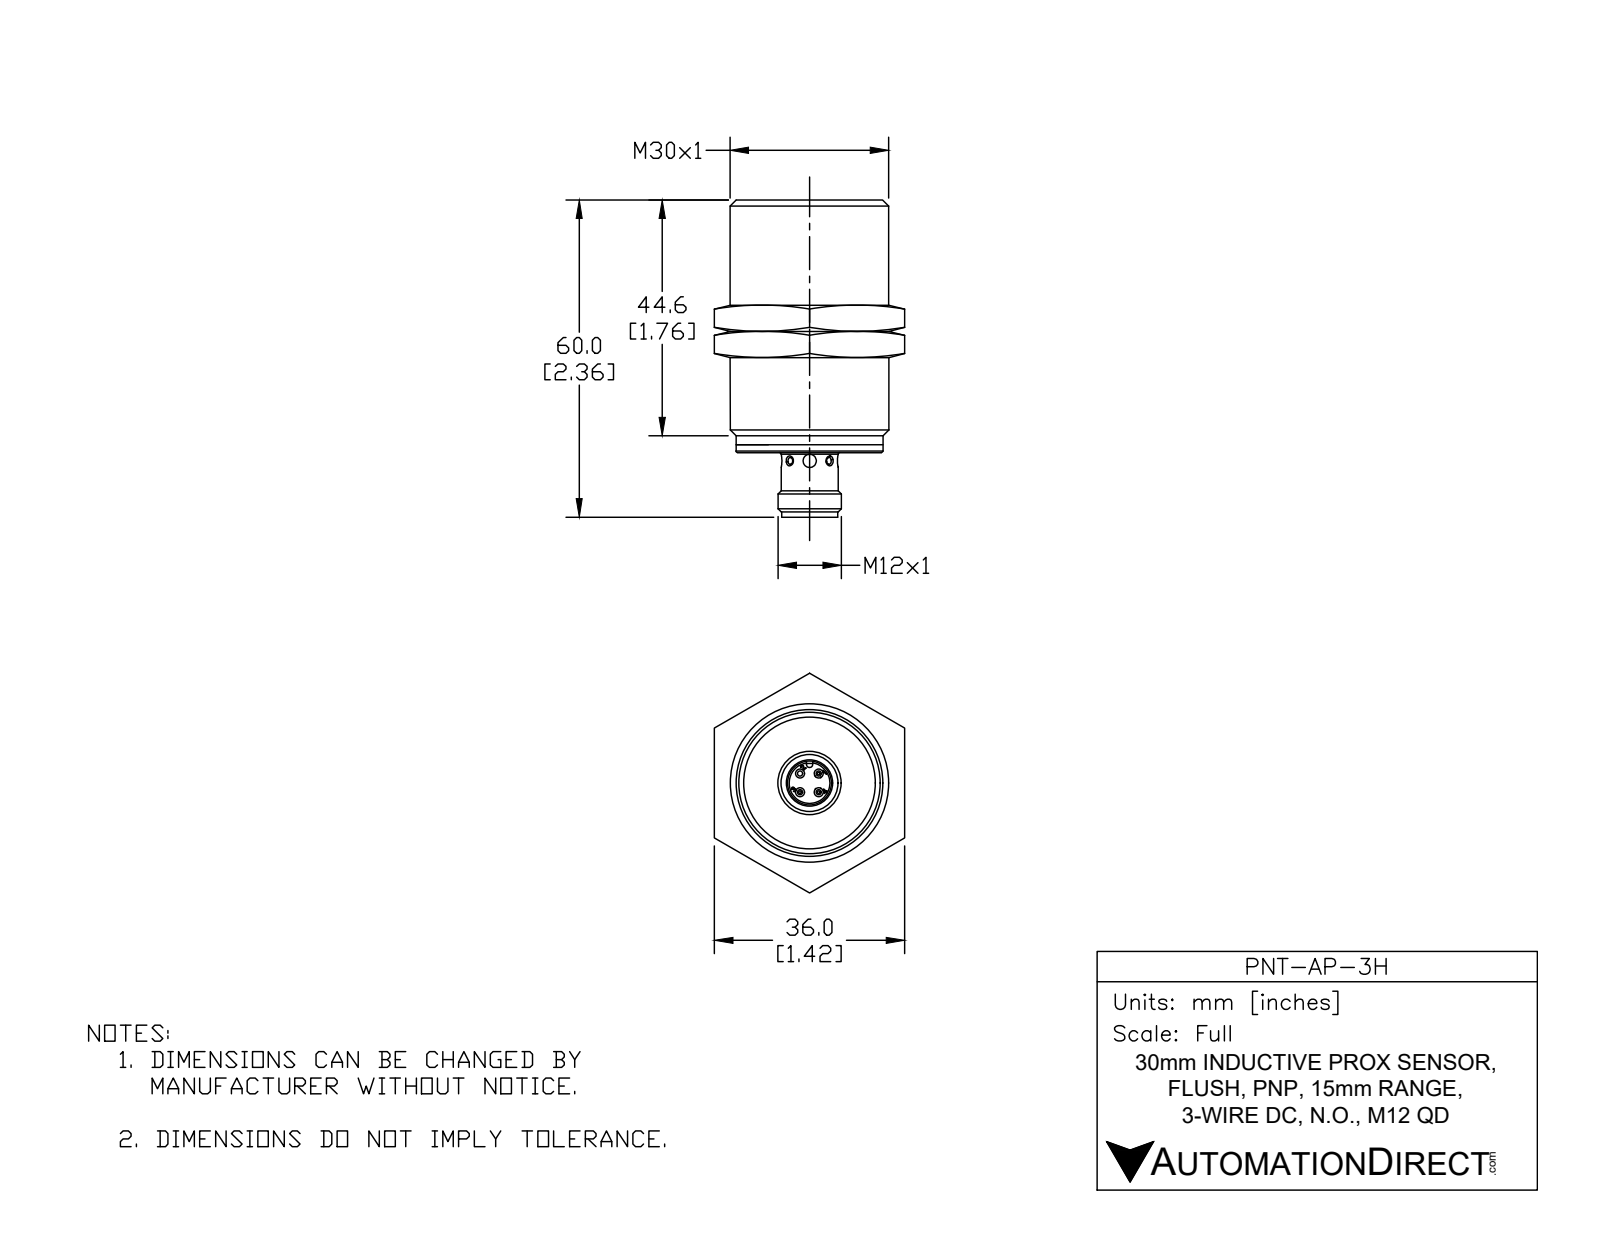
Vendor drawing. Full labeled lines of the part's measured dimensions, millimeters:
Part name (STEP PRODUCT): PNT-AP-3H
STEP written by: SolidWorks 2017 (AUTOMOTIVE_DESIGN)
Units: millimetres
Bodies: 1 solid, 660 faces (260 planar, 164 cylindrical, 236 other)
Overall size (bounding box): 60 × 30 × 30
Volume: 31 690 mm³ · Surface area: 16 240 mm²
Round holes (diameter × count): ⌀1.1 ×3, ⌀1 ×2, ⌀2.5 ×2, ⌀1 ×1, ⌀1 ×1, ⌀8.2 ×1, ⌀8.3 ×1, ⌀10 ×1, ⌀26.6 ×1, ⌀27.3 ×1
Round bosses / shafts (diameter × count): ⌀1 ×9, ⌀30 ×1, ⌀27.8 ×1, ⌀27.5 ×1, ⌀27.3 ×1, ⌀26.5 ×1, ⌀26.3 ×1, ⌀25.9 ×1
Partial cylindrical surfaces — rounded edges, fillets, slot ends (radius × count): R0.1 ×12, R0.5 ×8, R4 ×6, R0.8 ×3, R1 ×3, R0.6 ×1, R0.8 ×1
Main face-to-face distances: 4, 47.8, 43.8, 0.9, 3, 46.8, 47.1, 3.3, 0.8, 0.7
Hole centre spacings: 2.5, 3.5, 5
